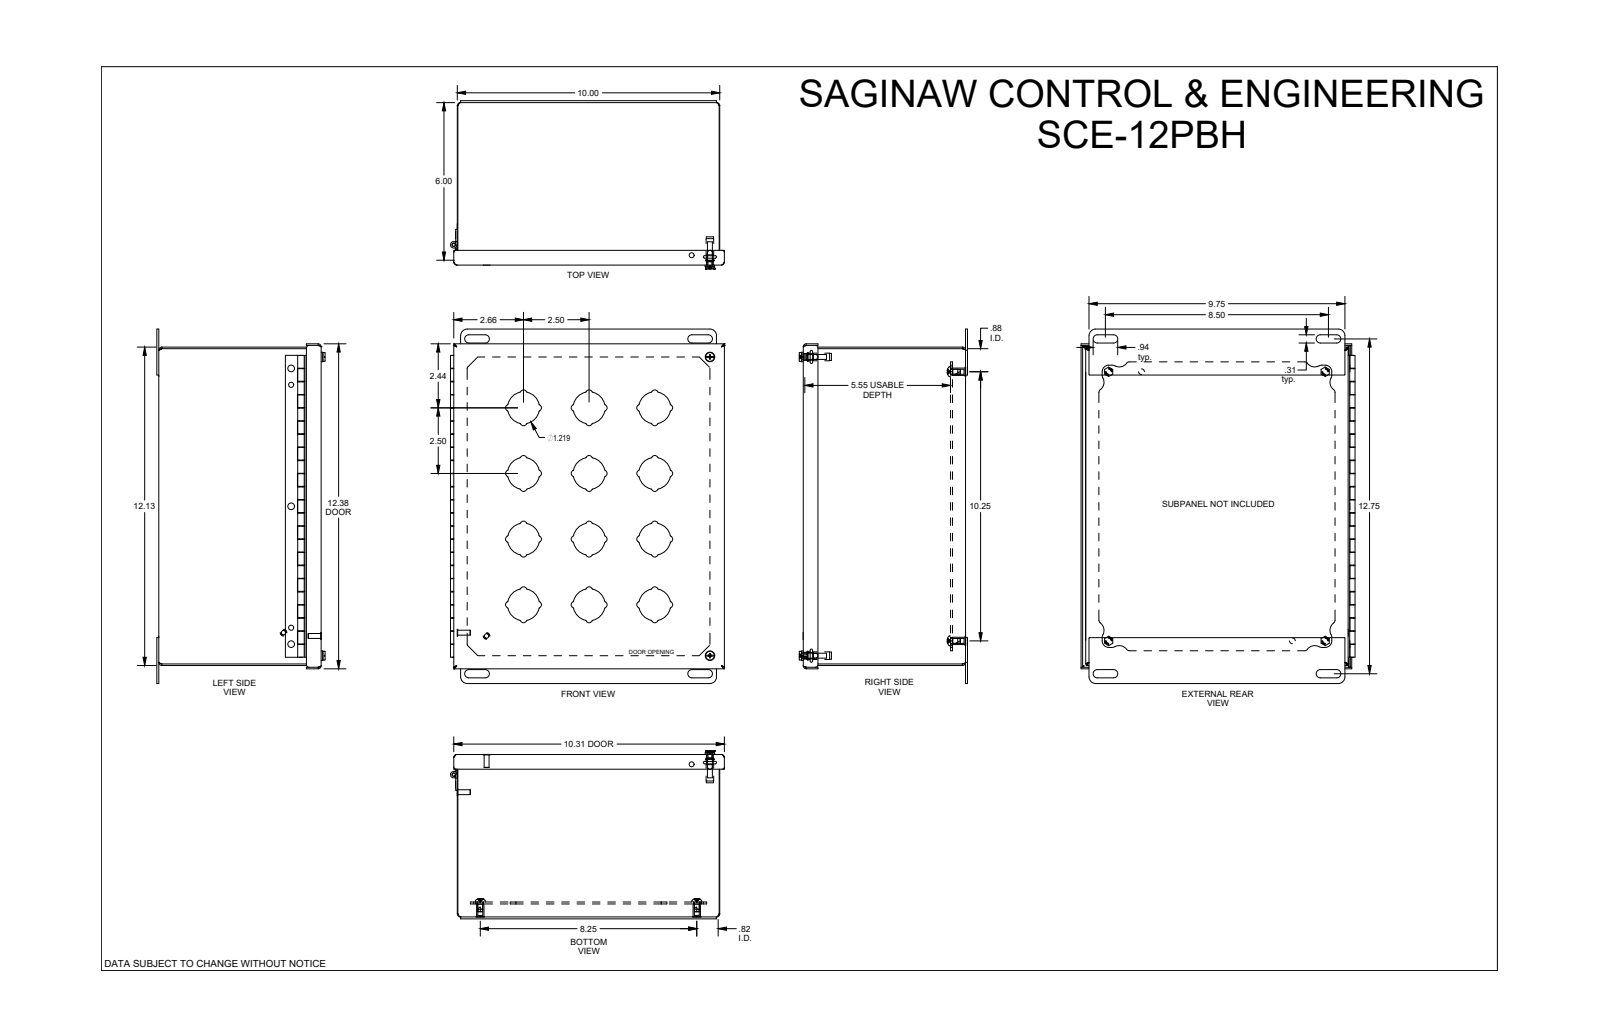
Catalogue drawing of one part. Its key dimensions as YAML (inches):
part_name: "SCE-12PBH"
step_written_by: "SolidWorks 2019 (AUTOMOTIVE_DESIGN)"
units: inches
bodies: {solids: 22, faces: 890, planar: 369, cylindrical: 453, other: 68}
overall_size: [13.5, 10.438, 6.322]
volume: 45.91
surface_area: 1437
round_holes:
  - {diameter: 0.19, count: 6}
  - {diameter: 0.25, count: 6}
  - {diameter: 0.281, count: 4}
  - {diameter: 0.317, count: 4}
  - {diameter: 0.126, count: 2}
  - {diameter: 0.218, count: 2}
  - {diameter: 0.22, count: 2}
  - {diameter: 0.266, count: 2}
  - {diameter: 0.193, count: 1}
round_bosses_or_shafts:
  - {diameter: 0.256, count: 5}
  - {diameter: 0.188, count: 5}
  - {diameter: 0.437, count: 4}
  - {diameter: 0.28, count: 4}
  - {diameter: 0.362, count: 2}
  - {diameter: 0.34, count: 2}
  - {diameter: 0.292, count: 2}
  - {diameter: 0.27, count: 2}
partial_cylinders:
  - {radius: 0.04, count: 96}
  - {radius: 0.125, count: 56}
  - {radius: 0.06, count: 20}
  - {radius: 0.25, count: 16}
  - {radius: 0.609, count: 12}
  - {radius: 0.063, count: 8}
  - {radius: 0.156, count: 8}
  - {radius: 0.344, count: 8}
face_to_face_distances: [0.06, 6.125, 9.94, 12.065, 6.185, 6.065, 0.075, 0.435, 0.51, 5.63]
hole_center_spacings: [8.768, 0.753, 13.909, 10.824, 13.158, 7, 8.25, 8.25]
